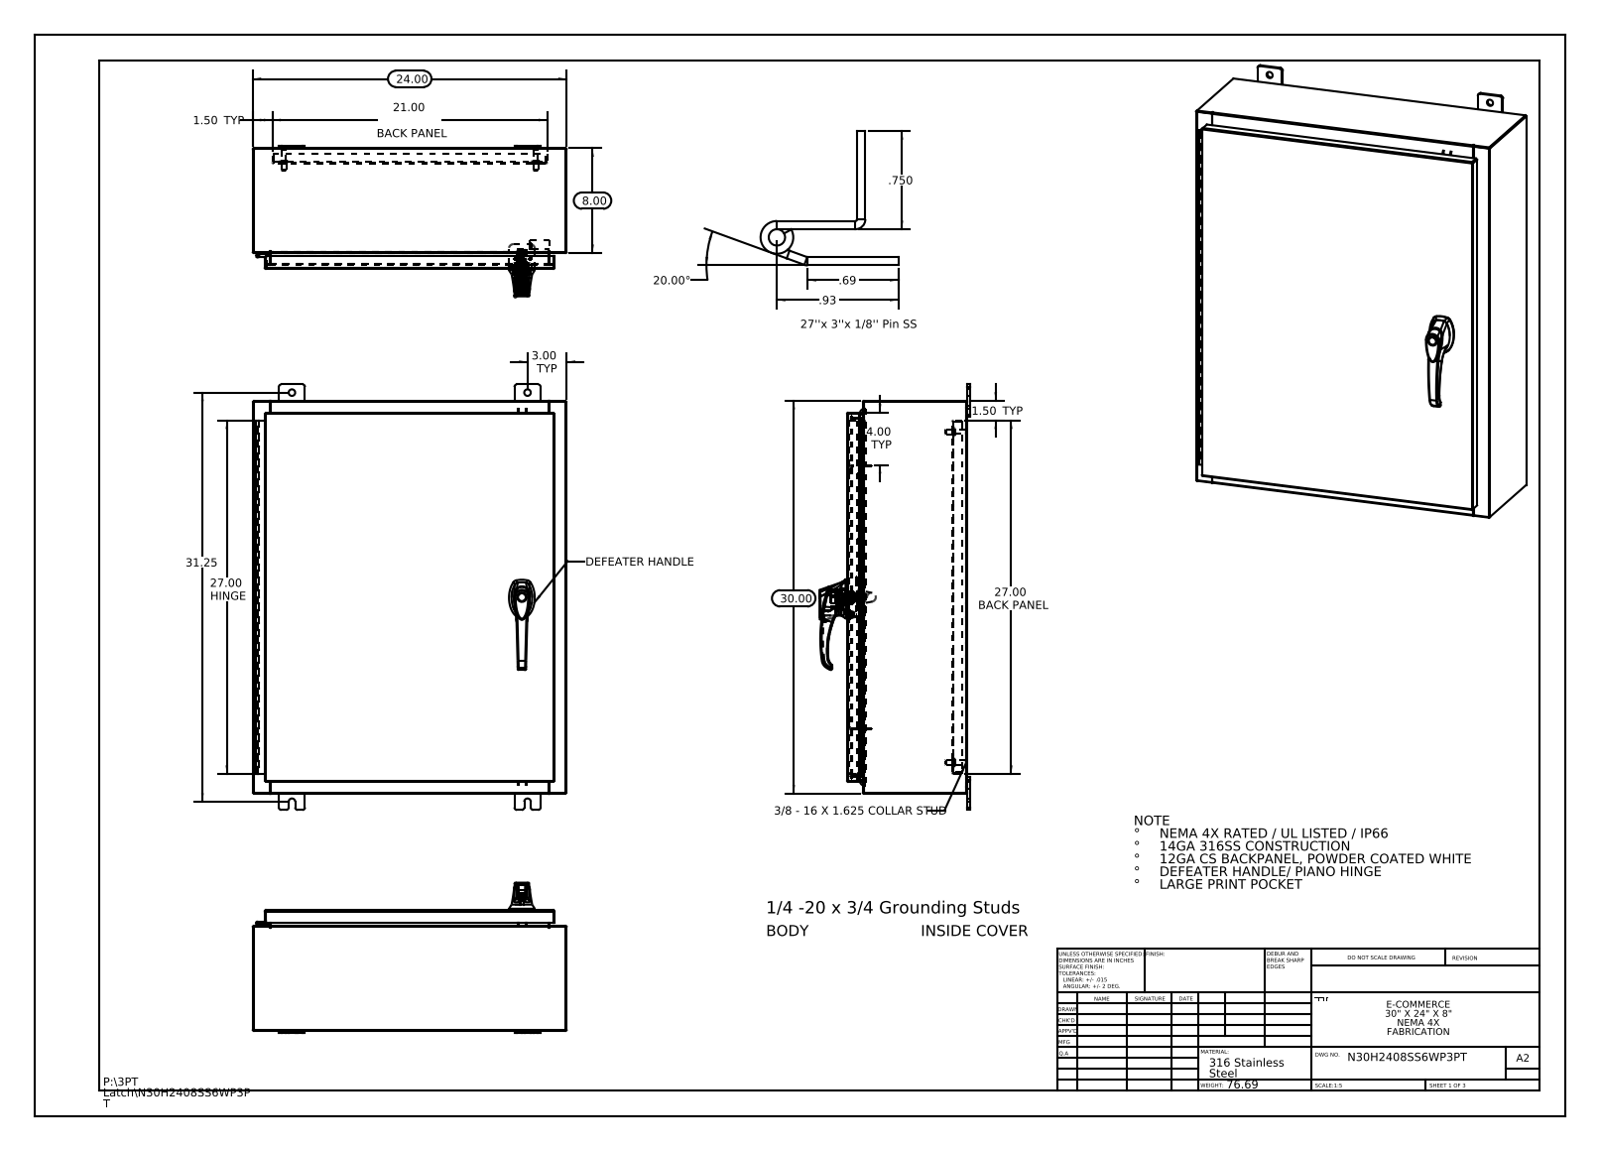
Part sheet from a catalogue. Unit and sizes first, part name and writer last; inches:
Units: inches
Overall size (bounding box): 32.5 × 24 × 11.495
Round holes (diameter × count): ⌀0.5 ×8, ⌀0.25 ×4, ⌀0.138 ×3, ⌀0.161 ×3, ⌀0.079 ×2, ⌀0.203 ×2, ⌀0.313 ×2, ⌀0.437 ×2, ⌀0.125 ×1, ⌀0.125 ×1, ⌀0.197 ×1, ⌀0.276 ×1
Round bosses / shafts (diameter × count): ⌀0.625 ×4, ⌀0.375 ×4, ⌀0.33 ×4, ⌀1.181 ×1, ⌀0.748 ×1, ⌀0.68 ×1, ⌀0.661 ×1, ⌀0.639 ×1
Partial cylindrical surfaces — rounded edges, fillets, slot ends (radius × count): R0.118 ×37, R0.006 ×33, R0.013 ×24, R0.19 ×24, R0.088 ×18, R0.039 ×15, R0.028 ×12, R0.008 ×6
Main face-to-face distances: 0.075, 9.126, 0.104, 9.051, 9.201, 1, 1.075, 8.051, 8.126, 1.179
Hole centre spacings: 8.369, 0.295, 0.625, 0.841, 1.25, 1.313, 1.561, 1.858
Volume: 272.1 in³ · Surface area: 6 712 in²
Bodies: 31 solids, 2576 faces (953 planar, 969 cylindrical, 654 other)
Part name (STEP PRODUCT): 00005310_26163101; N30H2408SS6WP3PT Top; N30H2408SS6WP3PT Backpanel; 022151 (+8 more)
STEP written by: SolidWorks 2013 (CONFIG_CONTROL_DESIGN)
